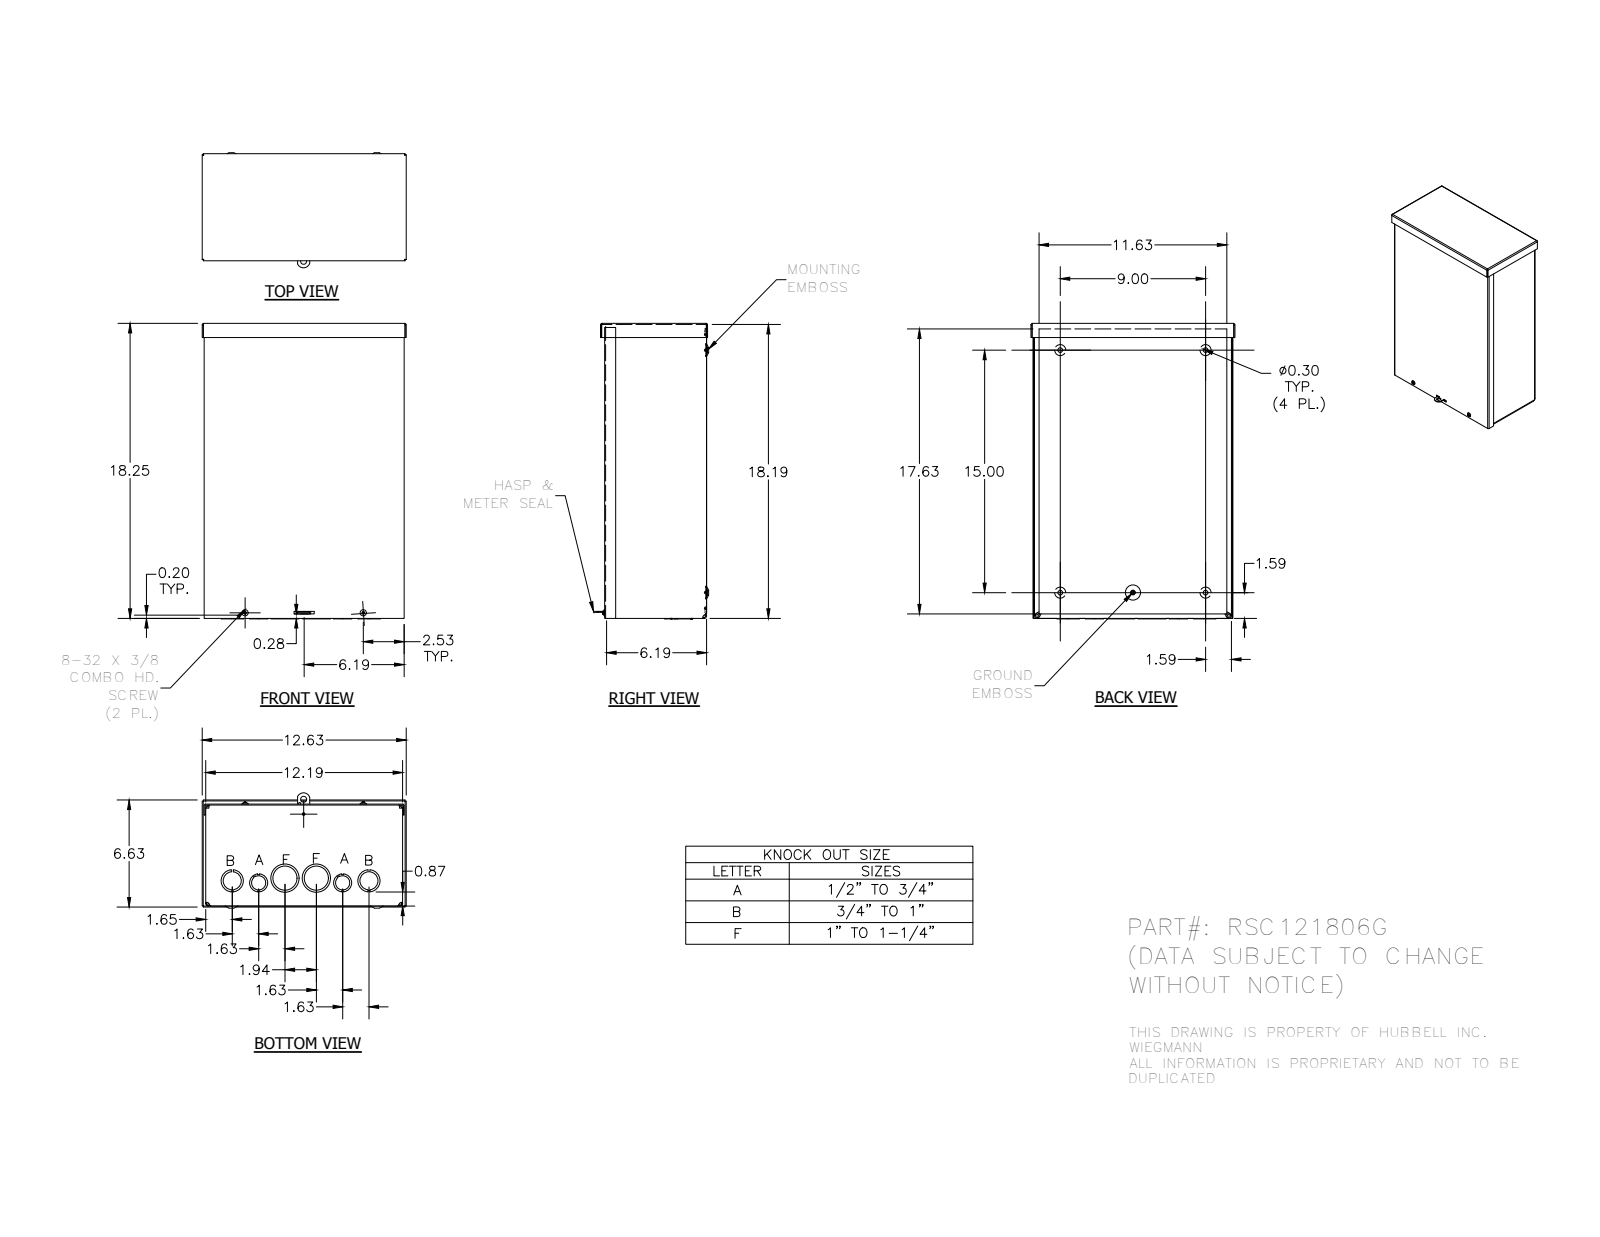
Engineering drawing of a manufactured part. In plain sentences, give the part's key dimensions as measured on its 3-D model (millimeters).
The part is named "RSC121806G_WRAP; RSC1218G_LID; RSC1206G_CAP; 3183 (+4 more)". Its 3-D file was written by "Autodesk Inventor 2014 (AUTOMOTIVE_DESIGN)". It is 7 solids with 551 faces: 264 planar, 143 cylindrical and 144 other. Overall it measures 464.32 by 320.68 by 180.97 millimeters. Its volume is 1 040 000 cubic millimeters and its surface area 1 334 000 square millimeters. Round holes: 4 of diameter 7.62, 4 of diameter 7.95, 4 of diameter 28.57, 2 of diameter 3.17, 2 of diameter 3.76, 2 of diameter 22.22, 2 of diameter 34.92, 2 of diameter 38.1, 2 of diameter 44.45, 1 of diameter 3.96, 1 of diameter 4.19, 1 of diameter 9.52. Round bosses or shafts: 2 of diameter 9.75, 2 of diameter 4.17, 1 of diameter 5.8. Partial cylindrical surfaces (rounded edges, fillets, slot ends): 14 of radius 0.25, 8 of radius 0.79, 8 of radius 2.37, 8 of radius 3.17, 8 of radius 4.75, 6 of radius 0.79, 4 of radius 1.4, 4 of radius 1.57. The main face-to-face distances are 1.58, 158.73, 157.15, 1.57, 307.99, 1.59, 160.32, 158.74, 460.39, 3.15. The hole center spacings are 34.43, 41.52, 42.07, 82.91, 90.99, 114.3, 132.15, 173.51.
